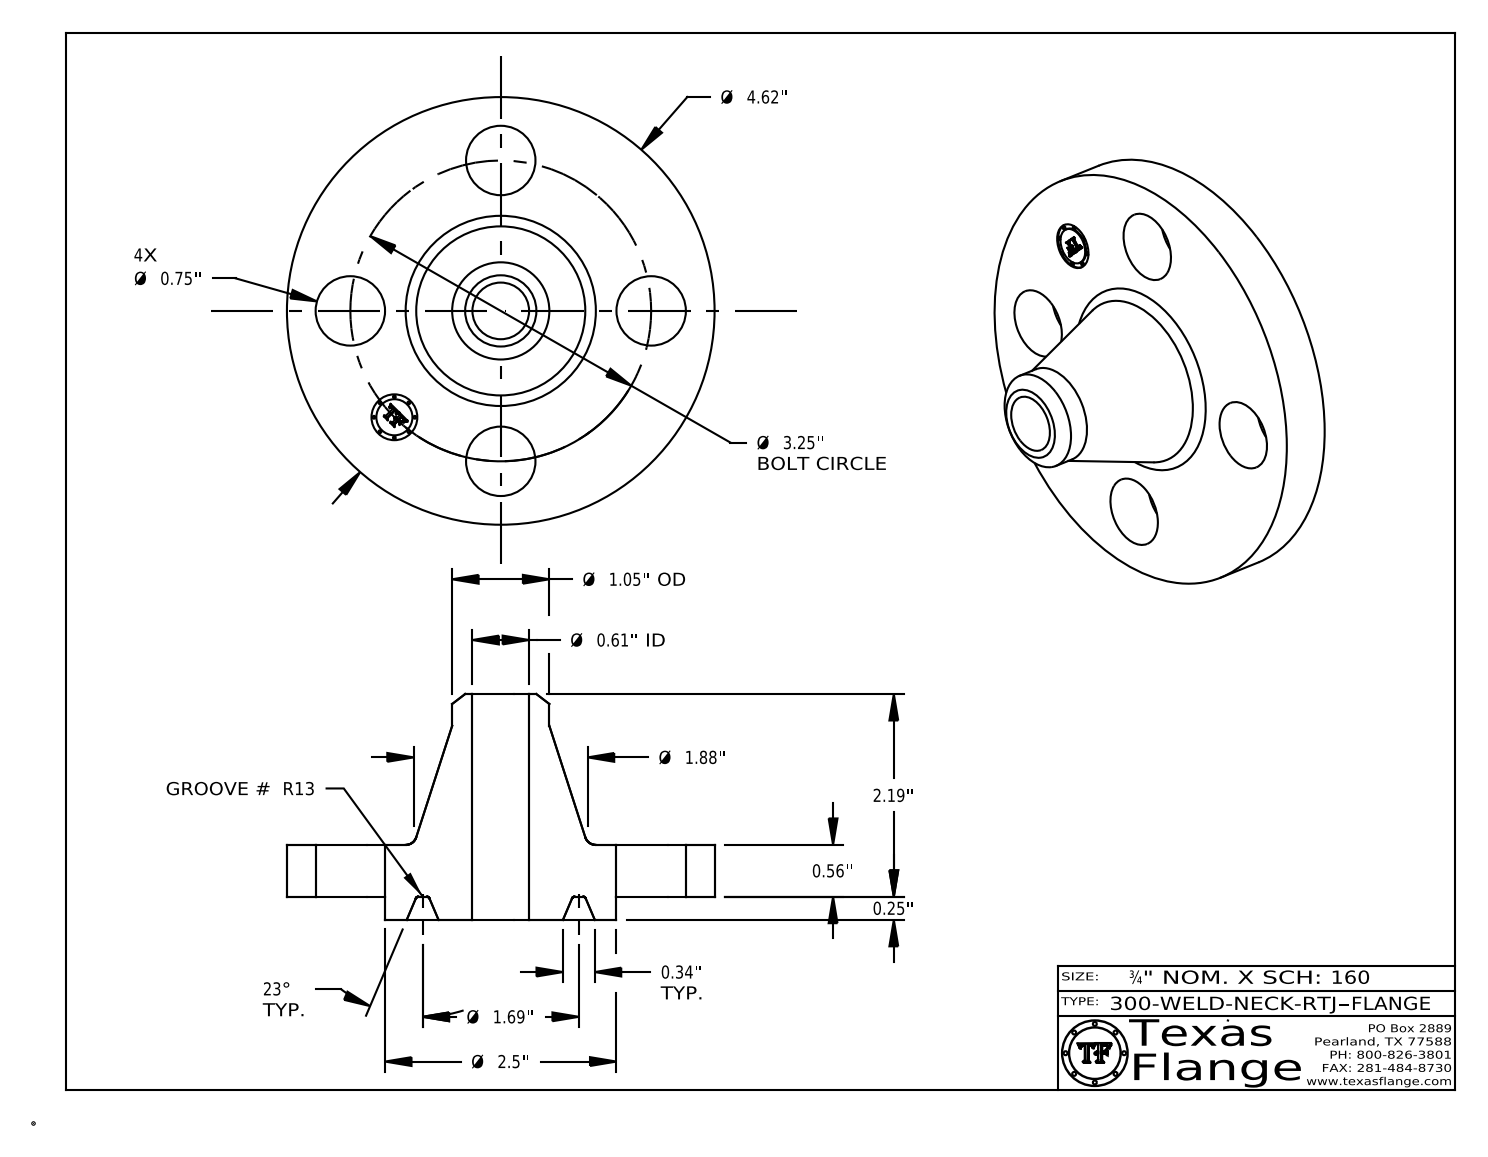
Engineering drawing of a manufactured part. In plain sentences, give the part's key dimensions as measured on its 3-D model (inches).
The part is named "300-WELD-NECK-RTJ". Its 3-D file was written by "CATIA V5 STEP AP214 (AUTOMOTIVE_DESIGN)". It is 1 solid with 421 faces: 371 planar, 36 cylindrical and 14 other. Overall it measures 4.62 by 4.62 by 2.44 inches. Its volume is 11.1 cubic inches and its surface area 56.32 square inches. Round holes: 4 of diameter 0.75, 1 of diameter 0.495, 1 of diameter 0.612. Round bosses or shafts: 8 of diameter 0.03, 1 of diameter 4.62, 1 of diameter 2.5, 1 of diameter 1.05, 1 of diameter 0.39. The main face-to-face distances are 0.56, 0.25, 0.81, 2.44, 2.19, 1.63, 0.795, 0.545, 0.015, 1.645. The hole center spacings are 1.625, 2.298, 1.244, 3.003, 3.25.
